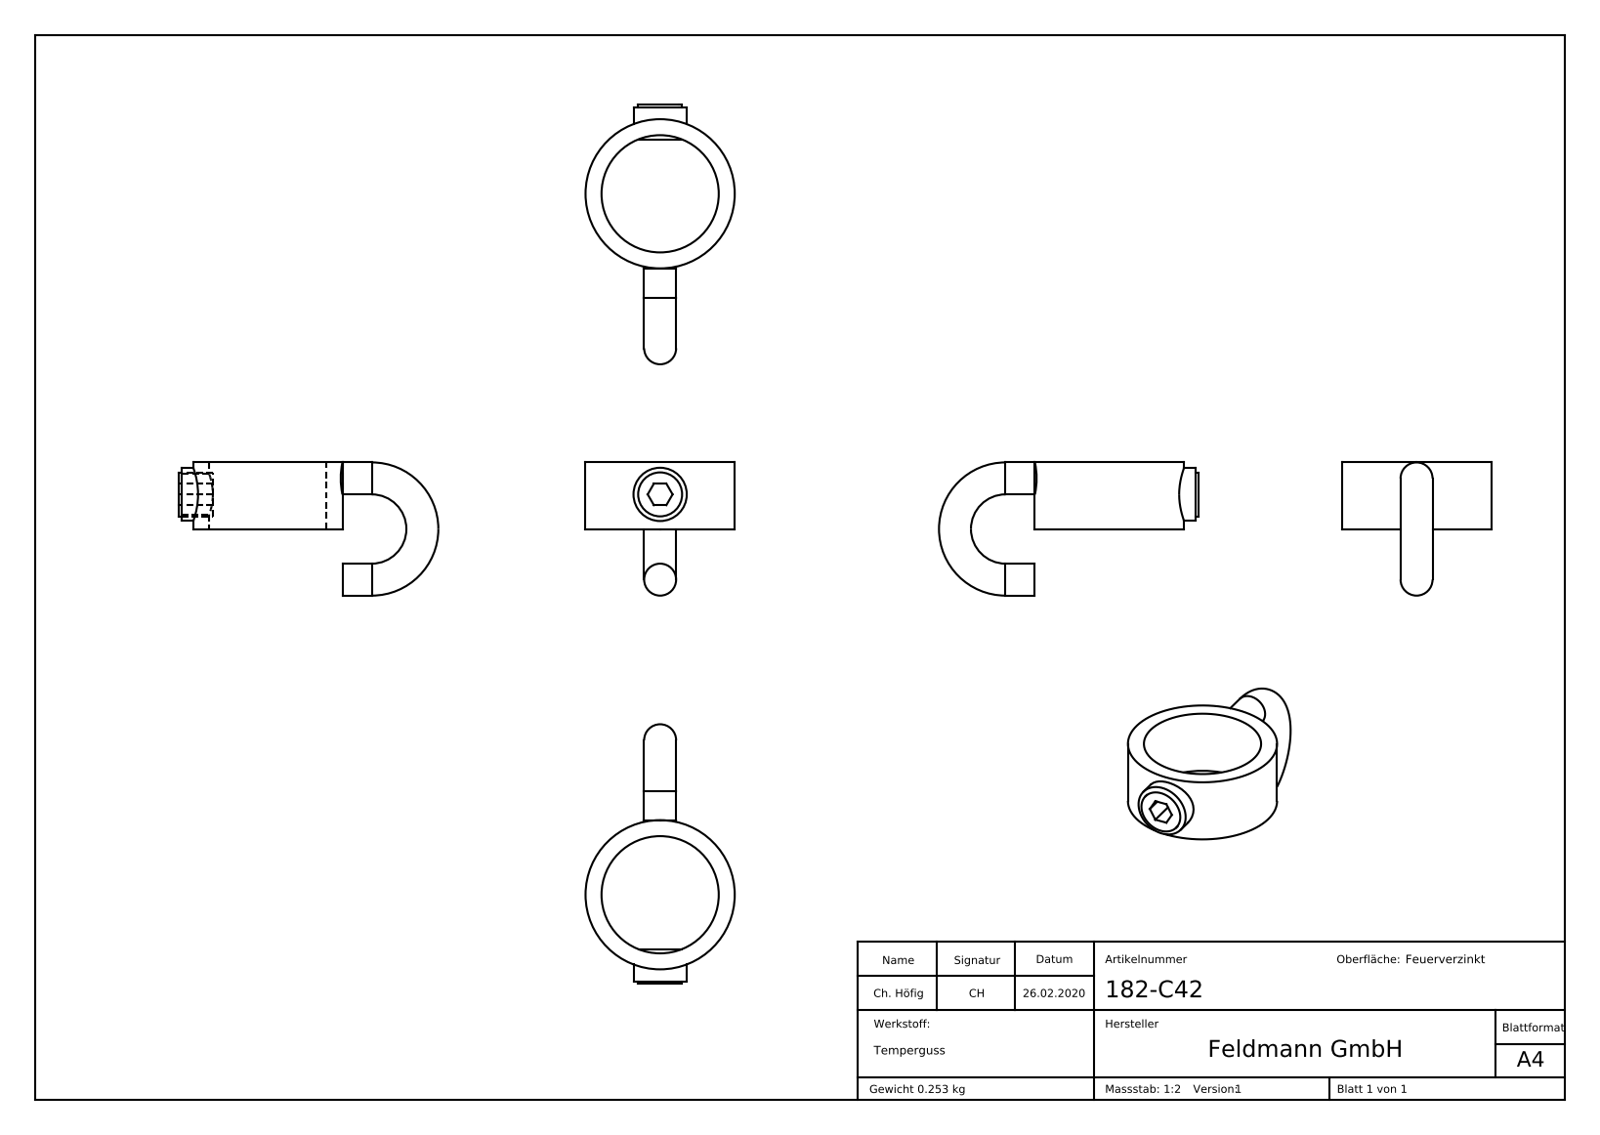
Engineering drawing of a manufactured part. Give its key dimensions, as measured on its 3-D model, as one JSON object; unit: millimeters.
{"part_name": "182-C42 Teil2; 182-C42 Teil1; 182-C42", "step_written_by": "SolidWorks 2018 (CONFIG_CONTROL_DESIGN)", "units": "millimeters", "bodies": {"solids": 2, "faces": 248, "planar": 103, "cylindrical": 40, "other": 105}, "overall_size": [97.5, 56, 50], "volume_mm3": 33906, "surface_area_mm2": 14034, "round_holes": [[15.25, 1], [44, 1]], "round_bosses_or_shafts": [[12, 2], [56, 1], [20, 1], [16.5, 1]], "partial_cylinders_radius": [[2, 12], [22.1, 1]], "face_to_face_distances": [25, 8.1, 12, 13, 1, 8.95, 17.05, 16.05, 7.95, 48.5]}
